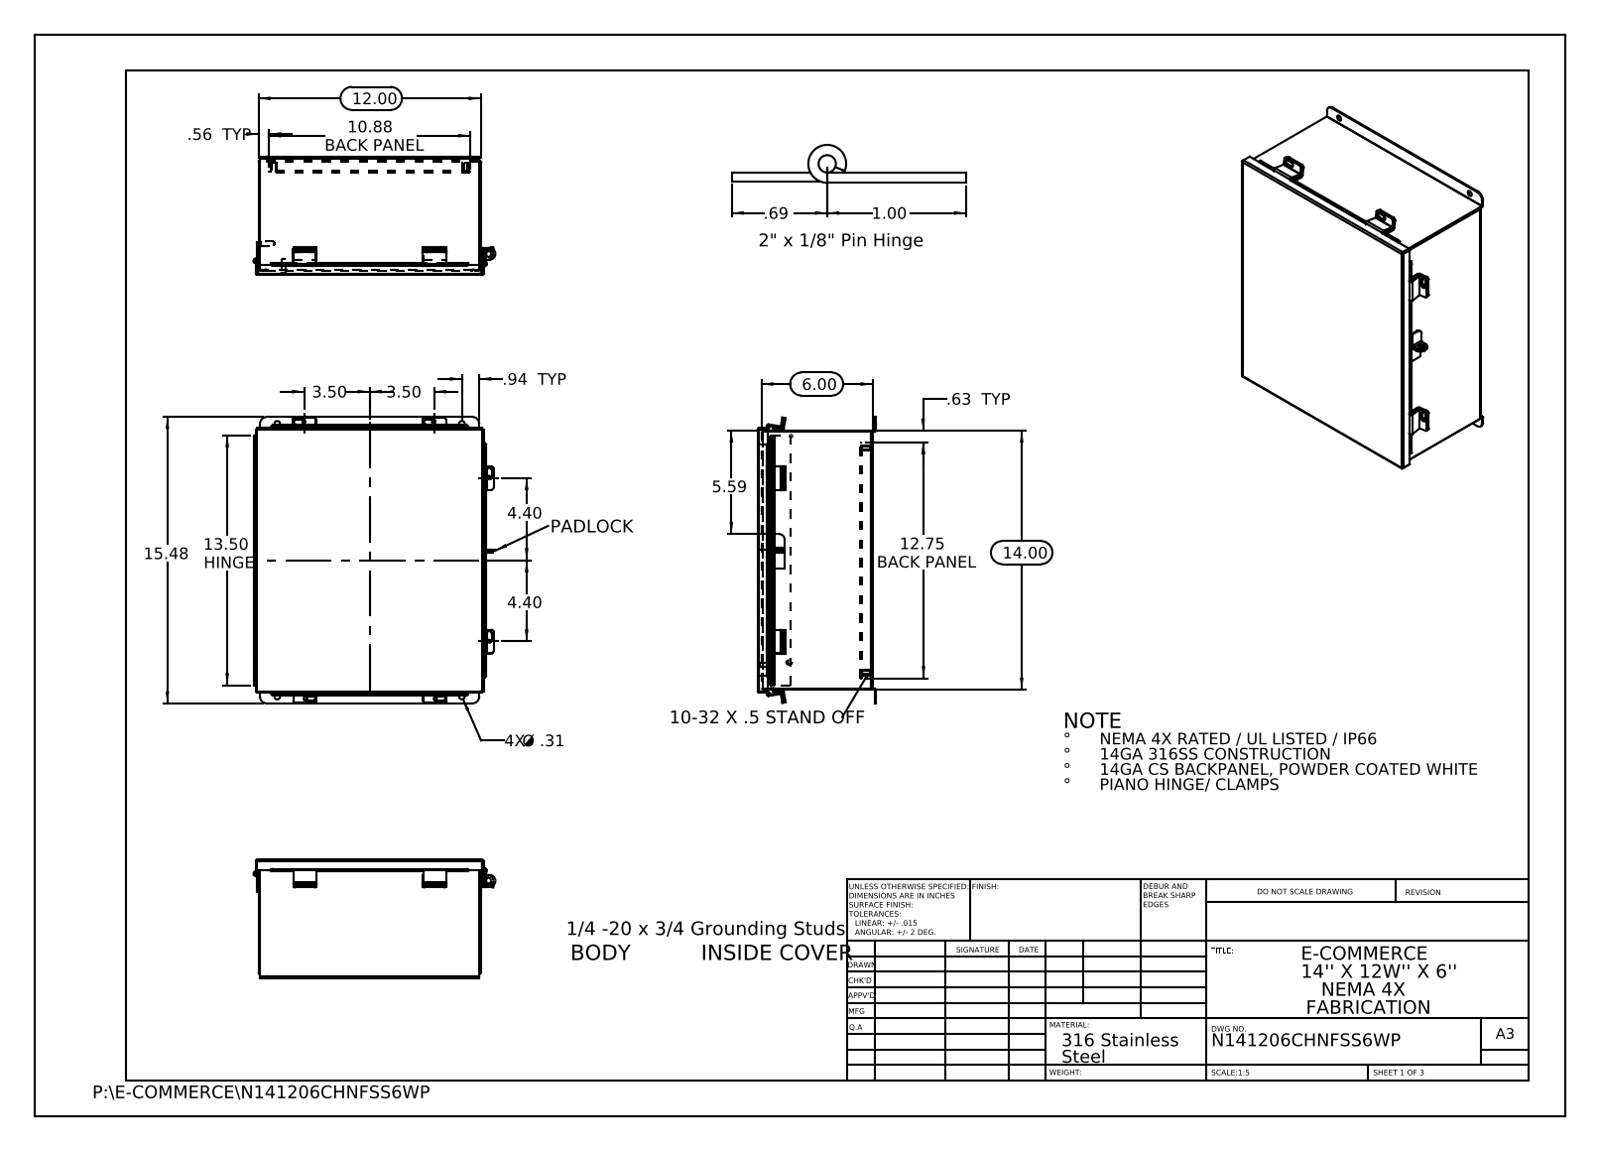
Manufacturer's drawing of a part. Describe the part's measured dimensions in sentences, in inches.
The part is named "N141206CHNFSS6WP JIC Clamp Bracket; N141206CHNFSS6WP Hinge Body Side; N141206CHNFSS6WP JIC_Cover_Template; N141206CHNFSS6WP JIC Backpanel (+8 more)". Its 3-D file was written by "SolidWorks 2013 (CONFIG_CONTROL_DESIGN)". It is 27 solids with 830 faces: 519 planar, 291 cylindrical and 20 other. Overall it measures 15.476 by 13.072 by 6.39 inches. Its volume is 67.44 cubic inches and its surface area 1 838 square inches. Round holes: 10 of diameter 0.25, 4 of diameter 0.187, 4 of diameter 0.312, 1 of diameter 0.125, 1 of diameter 0.125, 1 of diameter 0.373, 1 of diameter 0.375. Round bosses or shafts: 4 of diameter 0.313, 2 of diameter 0.315, 2 of diameter 0.236, 1 of diameter 0.273, 1 of diameter 0.25. Partial cylindrical surfaces (rounded edges, fillets, slot ends): 21 of radius 0.125, 13 of radius 0.013, 12 of radius 0.009, 12 of radius 0.088, 12 of radius 0.133, 6 of radius 0.083, 6 of radius 0.1, 4 of radius 0.375. The main face-to-face distances are 0.075, 6.128, 6.053, 6.203, 11.925, 13.925, 0.074, 0.575, 0.5, 5.553. The hole center spacings are 1.315, 10.258, 13.428, 16.846, 7, 9.976, 10.375, 12.126.
